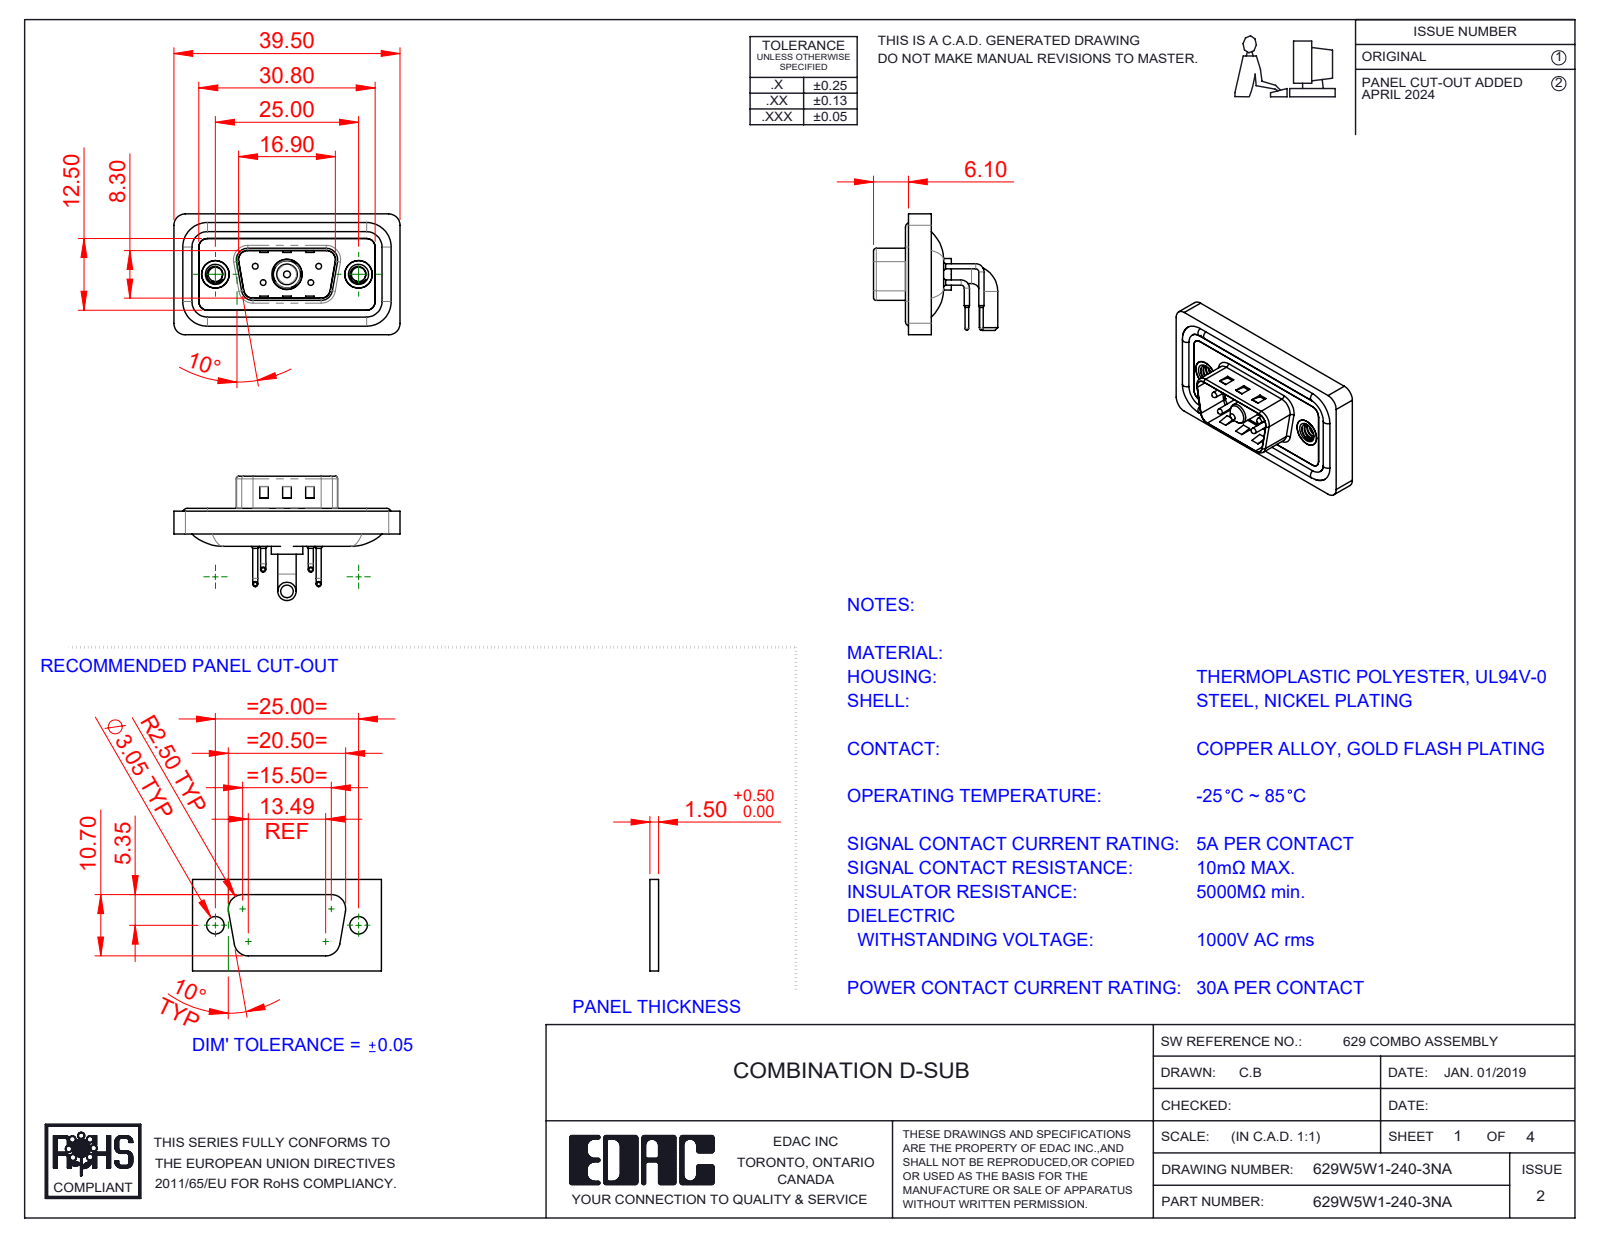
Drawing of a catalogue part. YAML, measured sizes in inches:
part_name: "629Combo Waterproof Housing_09 Contacts; 629Combo Threaded Rivet_A; 629Combo Shell Rear_09 Contacts; Power Pin_30A RA (+5 more)"
step_written_by: "SolidWorks 2023 (CONFIG_CONTROL_DESIGN)"
units: inches
bodies: {solids: 13, faces: 888, planar: 411, cylindrical: 343, other: 134}
overall_size: [1.555, 0.854, 0.831]
volume: 0.275
surface_area: 11.14
round_holes:
  - {diameter: 0.03, count: 4}
  - {diameter: 0.063, count: 4}
  - {diameter: 0.079, count: 4}
  - {diameter: 0.098, count: 2}
  - {diameter: 0.157, count: 2}
  - {diameter: 0.189, count: 2}
  - {diameter: 0.197, count: 2}
  - {diameter: 0.191, count: 1}
  - {diameter: 0.209, count: 1}
round_bosses_or_shafts:
  - {diameter: 0.035, count: 8}
  - {diameter: 0.063, count: 4}
  - {diameter: 0.059, count: 4}
  - {diameter: 0.039, count: 4}
  - {diameter: 0.026, count: 4}
  - {diameter: 0.193, count: 2}
  - {diameter: 0.126, count: 2}
  - {diameter: 0.217, count: 1}
partial_cylinders:
  - {radius: 0.059, count: 18}
  - {radius: 0.079, count: 18}
  - {radius: 0.02, count: 8}
  - {radius: 0.063, count: 8}
  - {radius: 0.01, count: 4}
  - {radius: 0.024, count: 4}
  - {radius: 0.026, count: 4}
  - {radius: 0.035, count: 4}
face_to_face_distances: [0.016, 0.114, 0.043, 0.031, 0.083, 0.098, 0.063, 0.122, 0.177, 0.059]
hole_center_spacings: [0.124, 0.225, 0.28, 0.492, 0.713, 0.173, 0.173, 0.327]
